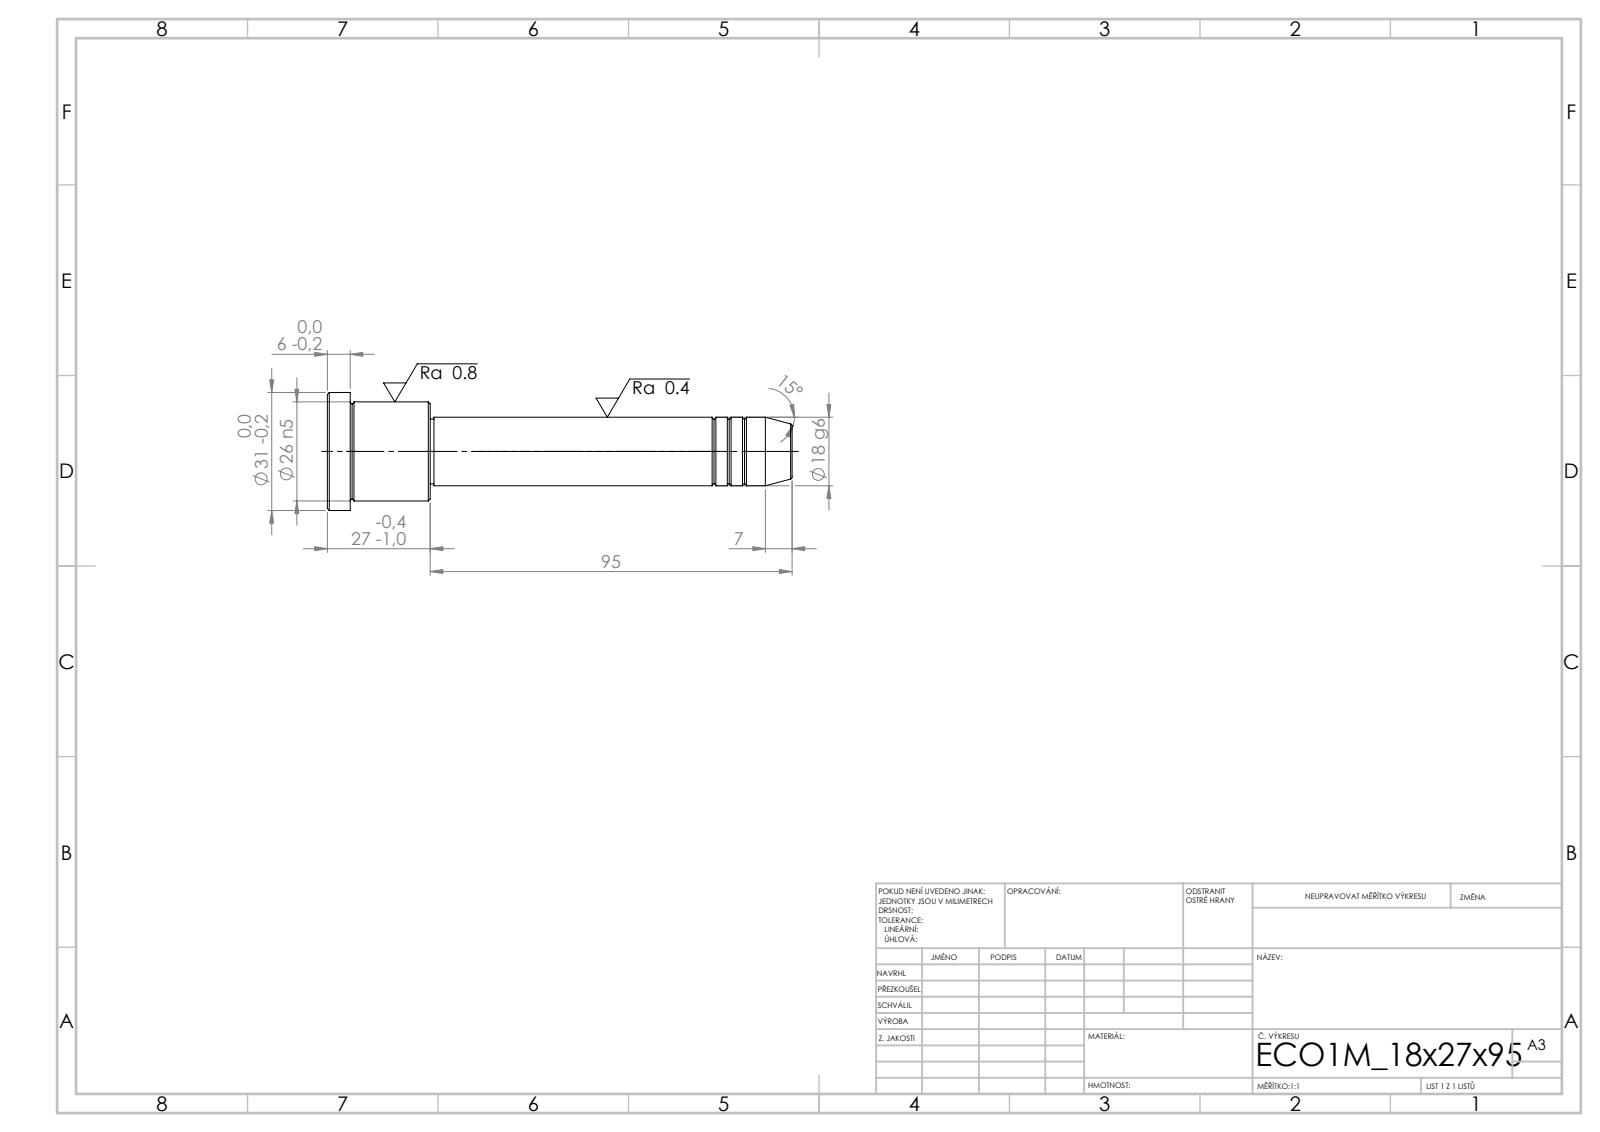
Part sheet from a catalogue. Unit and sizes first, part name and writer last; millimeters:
Units: millimetres
Overall size (bounding box): 122 × 31 × 31
Round bosses / shafts (diameter × count): ⌀31 ×1, ⌀26 ×1, ⌀18 ×1, ⌀17 ×1
Main face-to-face distances: 27, 21, 6, 95, 116, 122, 94, 1, 22, 28
Volume: 39 360 mm³ · Surface area: 9 182 mm²
Bodies: 1 solid, 43 faces (5 planar, 14 cylindrical, 24 other)
STEP written by: SolidWorks 2019 (CONFIG_CONTROL_DESIGN)
